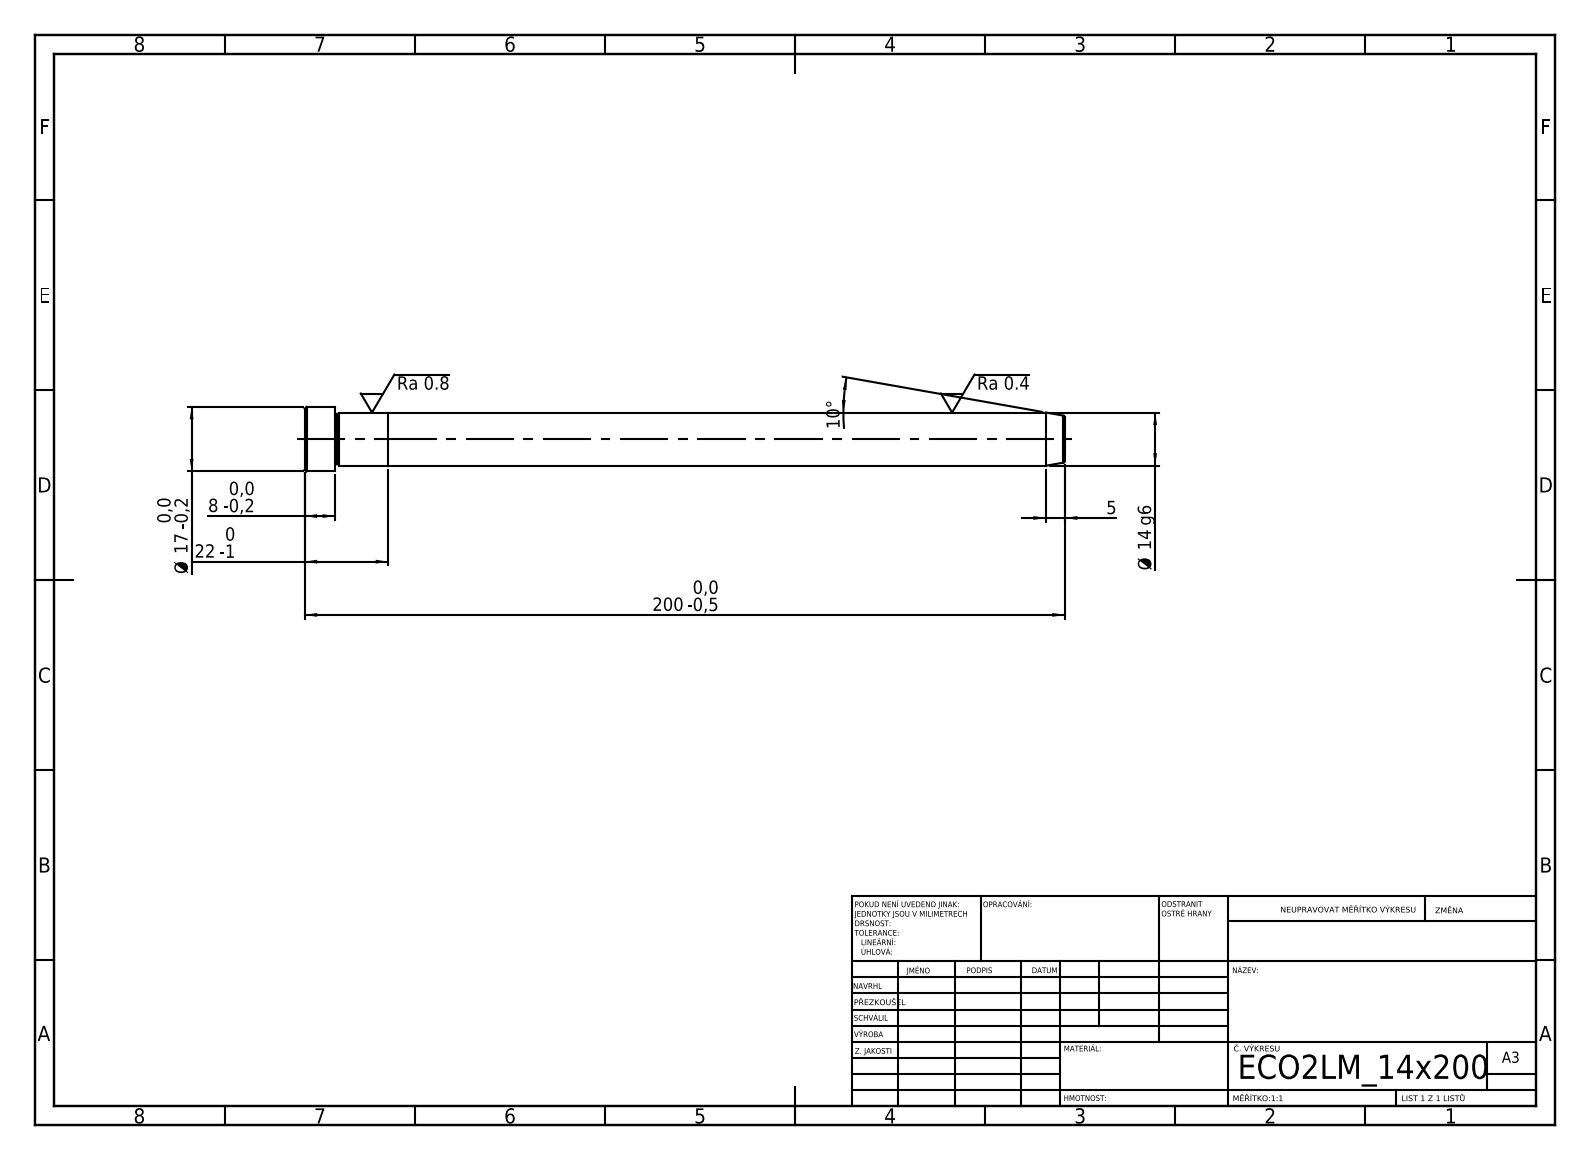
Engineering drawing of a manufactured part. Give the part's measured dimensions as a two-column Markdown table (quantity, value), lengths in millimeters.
| quantity | value |
| --- | --- |
| STEP written by | SolidWorks 2019 (CONFIG_CONTROL_DESIGN) |
| units | millimeters |
| bodies | 2 solids, 21 faces (5 planar, 6 cylindrical, 10 other) |
| overall size | 200 × 17 × 17 |
| volume | 31 254 mm³ |
| surface area | 9 587 mm² |
| round bosses / shafts (diameter × count) | 17 × 1, 14 × 1 |
| main face-to-face distances | 22, 178, 200, 192, 14, 8 |
